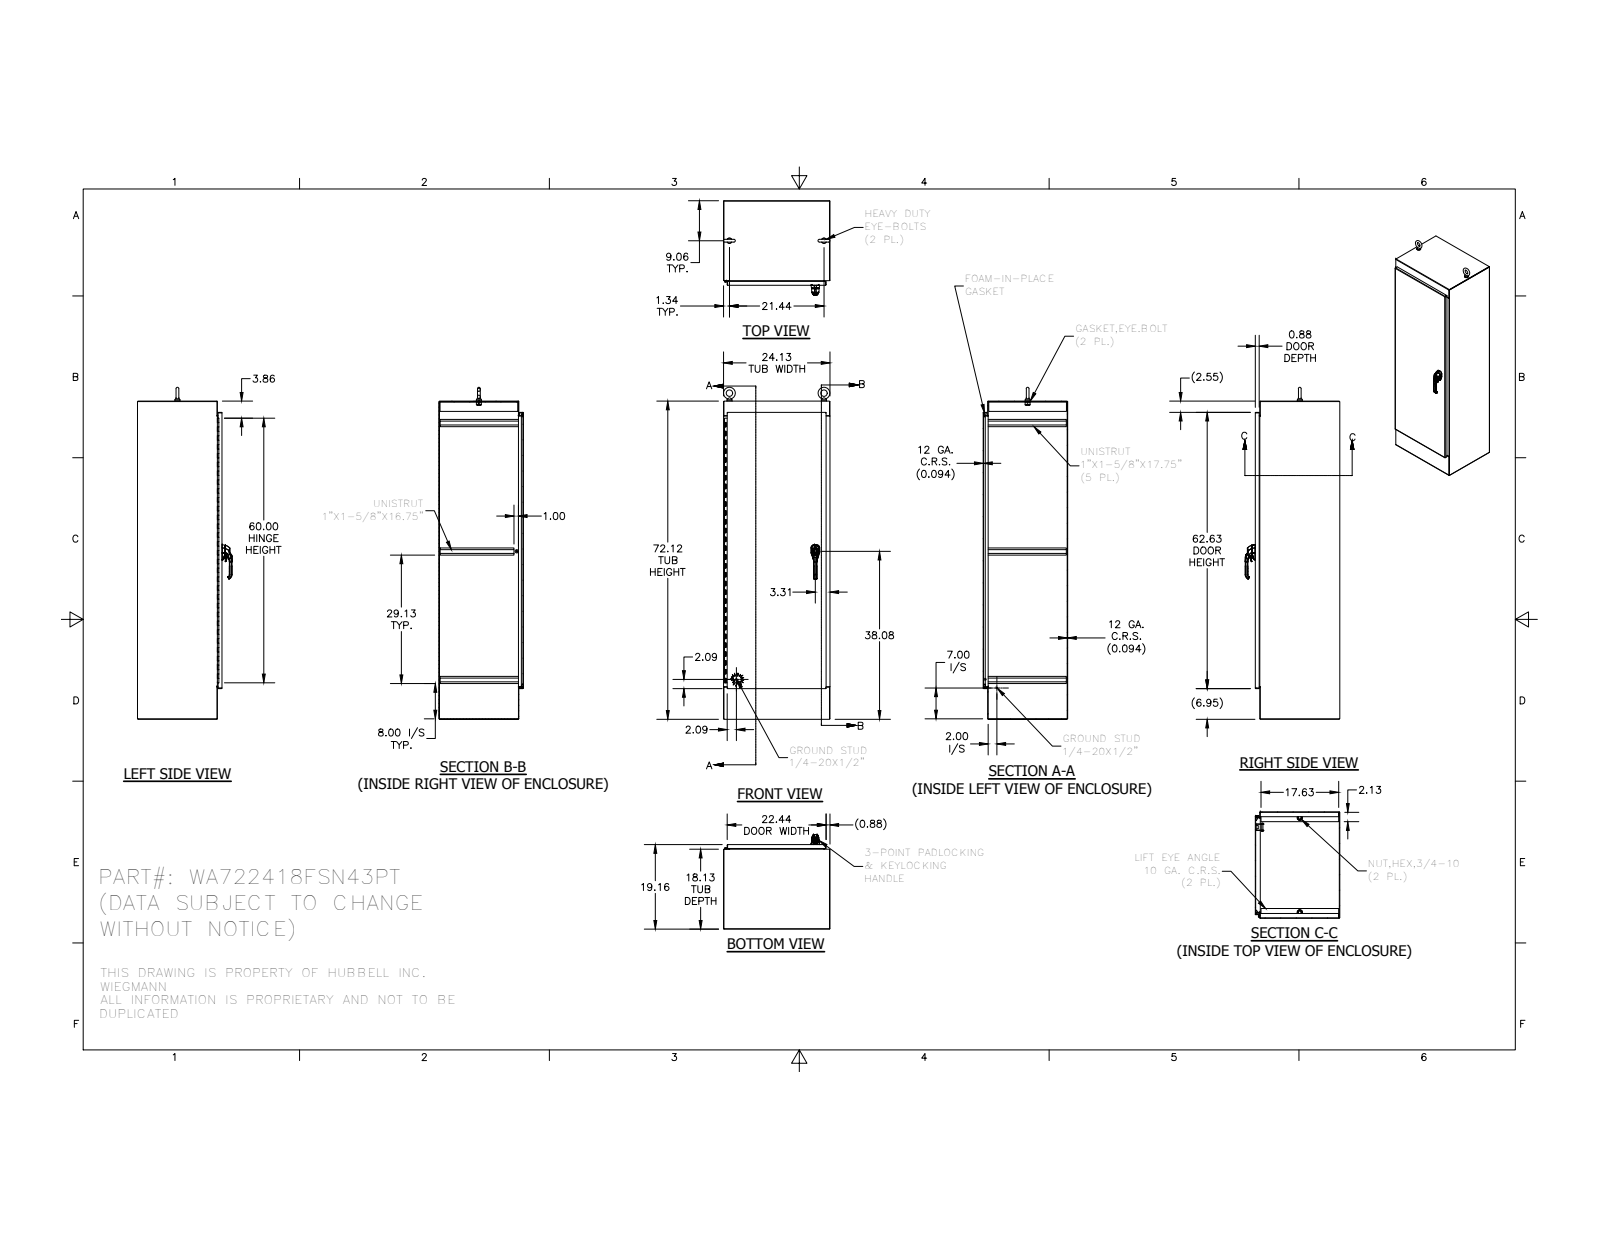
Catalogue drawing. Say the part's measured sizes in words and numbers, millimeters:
The part is named "37029; HSSN1300W60; SUPPORT-ROLL_AF0; WA7224FSN43PTDR (+8 more)". Its 3-D file was written by "SolidWorks 2014 (AUTOMOTIVE_DESIGN)". It is 51 solids with 1936 faces: 830 planar, 784 cylindrical and 322 other. Overall it measures 1911.3 by 612.8 by 486.7 millimeters. Its volume is 13 370 000 cubic millimeters and its surface area 10 840 000 square millimeters. Round holes: 8 of diameter 7, 4 of diameter 5.1, 3 of diameter 7.1, 2 of diameter 6.1, 2 of diameter 6.4, 2 of diameter 6.4, 2 of diameter 10.2, 2 of diameter 10.3, 2 of diameter 11.4, 2 of diameter 16.3, 2 of diameter 20.7, 1 of diameter 3.2. Round bosses or shafts: 3 of diameter 6.4, 2 of diameter 31.8, 2 of diameter 28.4, 2 of diameter 25.4, 2 of diameter 19.1, 2 of diameter 14.3, 2 of diameter 13.4, 2 of diameter 12.7. Partial cylindrical surfaces (rounded edges, fillets, slot ends): 17 of radius 0.8, 16 of radius 0.3, 15 of radius 3.2, 14 of radius 1.3, 12 of radius 0.5, 12 of radius 1.3, 12 of radius 2.2, 12 of radius 3.2. The main face-to-face distances are 2.4, 484.3, 610.4, 481.9, 608, 486.7, 612.8, 1829.6, 458, 26.3. The hole center spacings are 1376.6, 1395.6, 19.4, 19.4, 30.4, 32.3, 1385.8, 1386.1.
